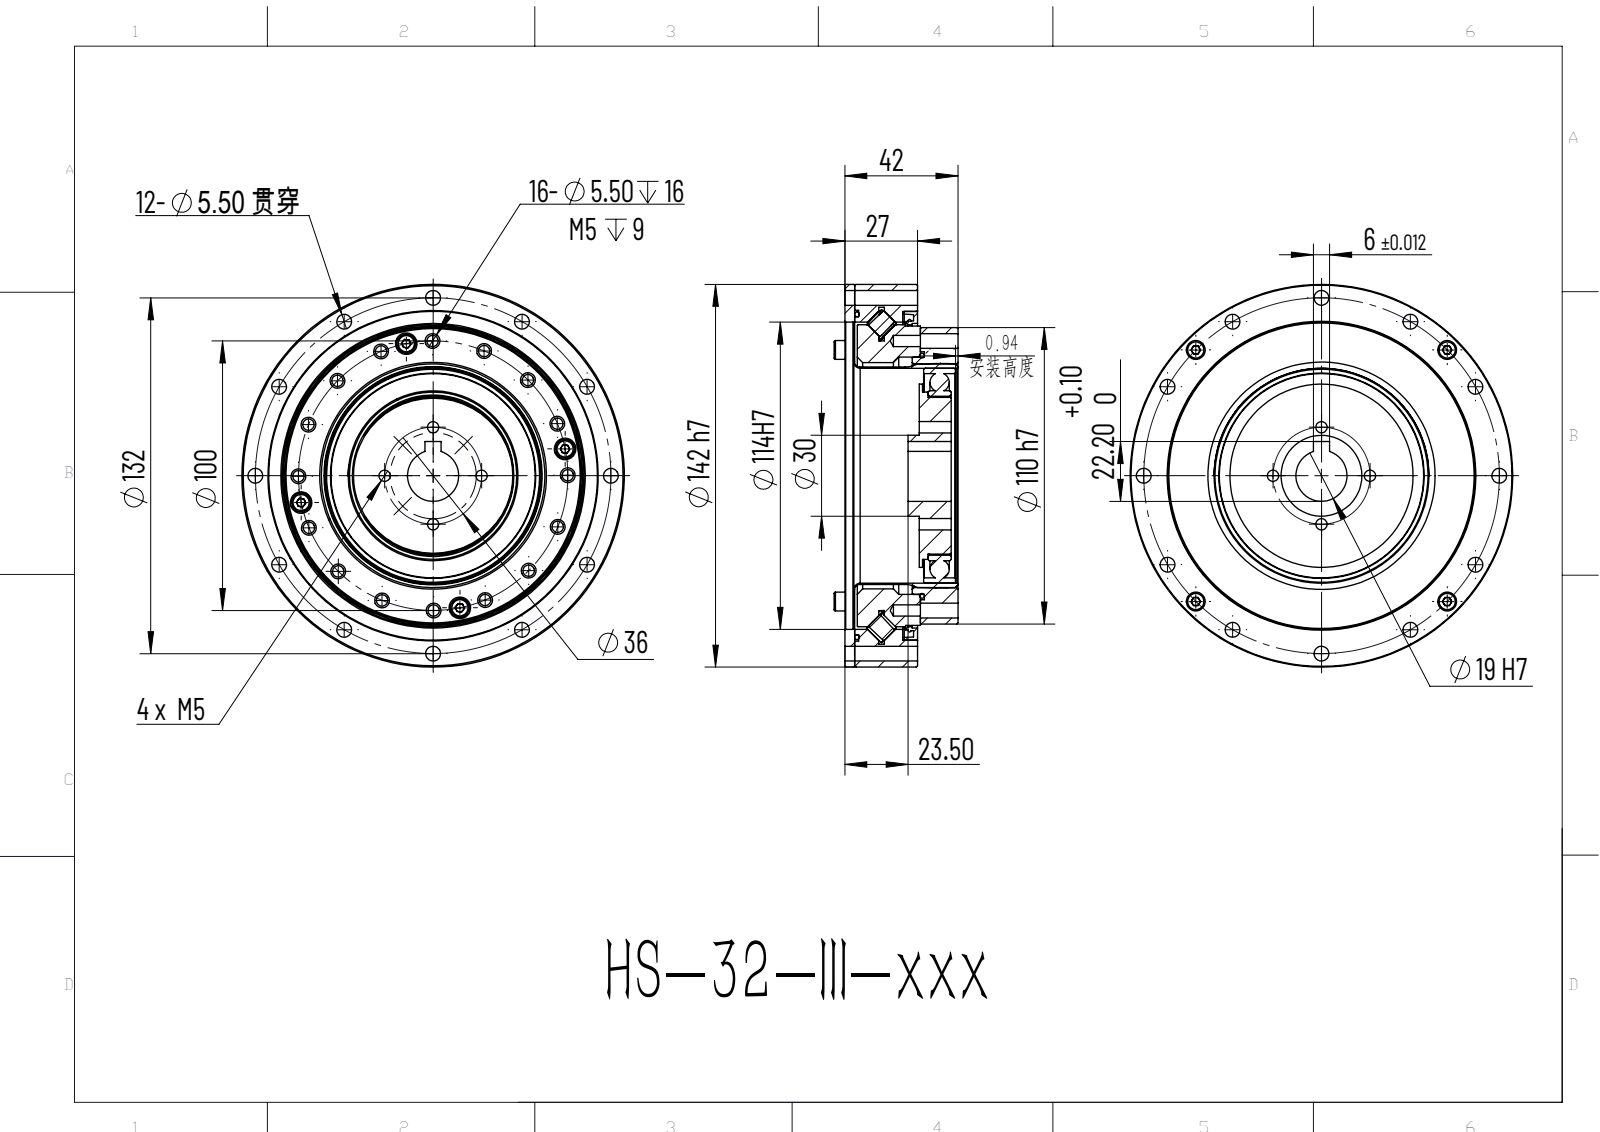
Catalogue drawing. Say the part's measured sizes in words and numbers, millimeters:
The part is named "HS-32-III; hexagon socket head cap screws gb_GB_FASTENER_SCREWS_HSHCS M4X12-C; ????-STXB-32080-01; O????-?90X?1.8_?? (+8 more)". Its 3-D file was written by "ONSHAPE BY PTC INC, 1.201 (AP242_MANAGED_MODEL_BASED_3D_ENGINEERING_MIM_LF)". It is 91 solids with 971 faces: 545 planar, 246 cylindrical and 180 other. Overall it measures 142 by 142 by 46 millimeters. Its volume is 342 771 cubic millimeters and its surface area 188 103 square millimeters. Round holes: 28 of diameter 5.5, 20 of diameter 4.2, 8 of diameter 3.3, 8 of diameter 4.5, 4 of diameter 8, 1 of diameter 2.5, 1 of diameter 3.4, 1 of diameter 6, 1 of diameter 19, 1 of diameter 58.93, 1 of diameter 75.81, 1 of diameter 79.75. Round bosses or shafts: 36 of diameter 8, 8 of diameter 7, 8 of diameter 4, 1 of diameter 142, 1 of diameter 118, 1 of diameter 112, 1 of diameter 111, 1 of diameter 110. Partial cylindrical surfaces (rounded edges, fillets, slot ends): 36 of radius 4, 36 of radius 4.03. The main face-to-face distances are 1, 23.4, 24.4, 3.6, 27, 28, 3.33, 23.67, 24.67, 15. The hole center spacings are 66, 93.34, 19.51, 50, 34.16, 38.27, 65.99, 70.71.
